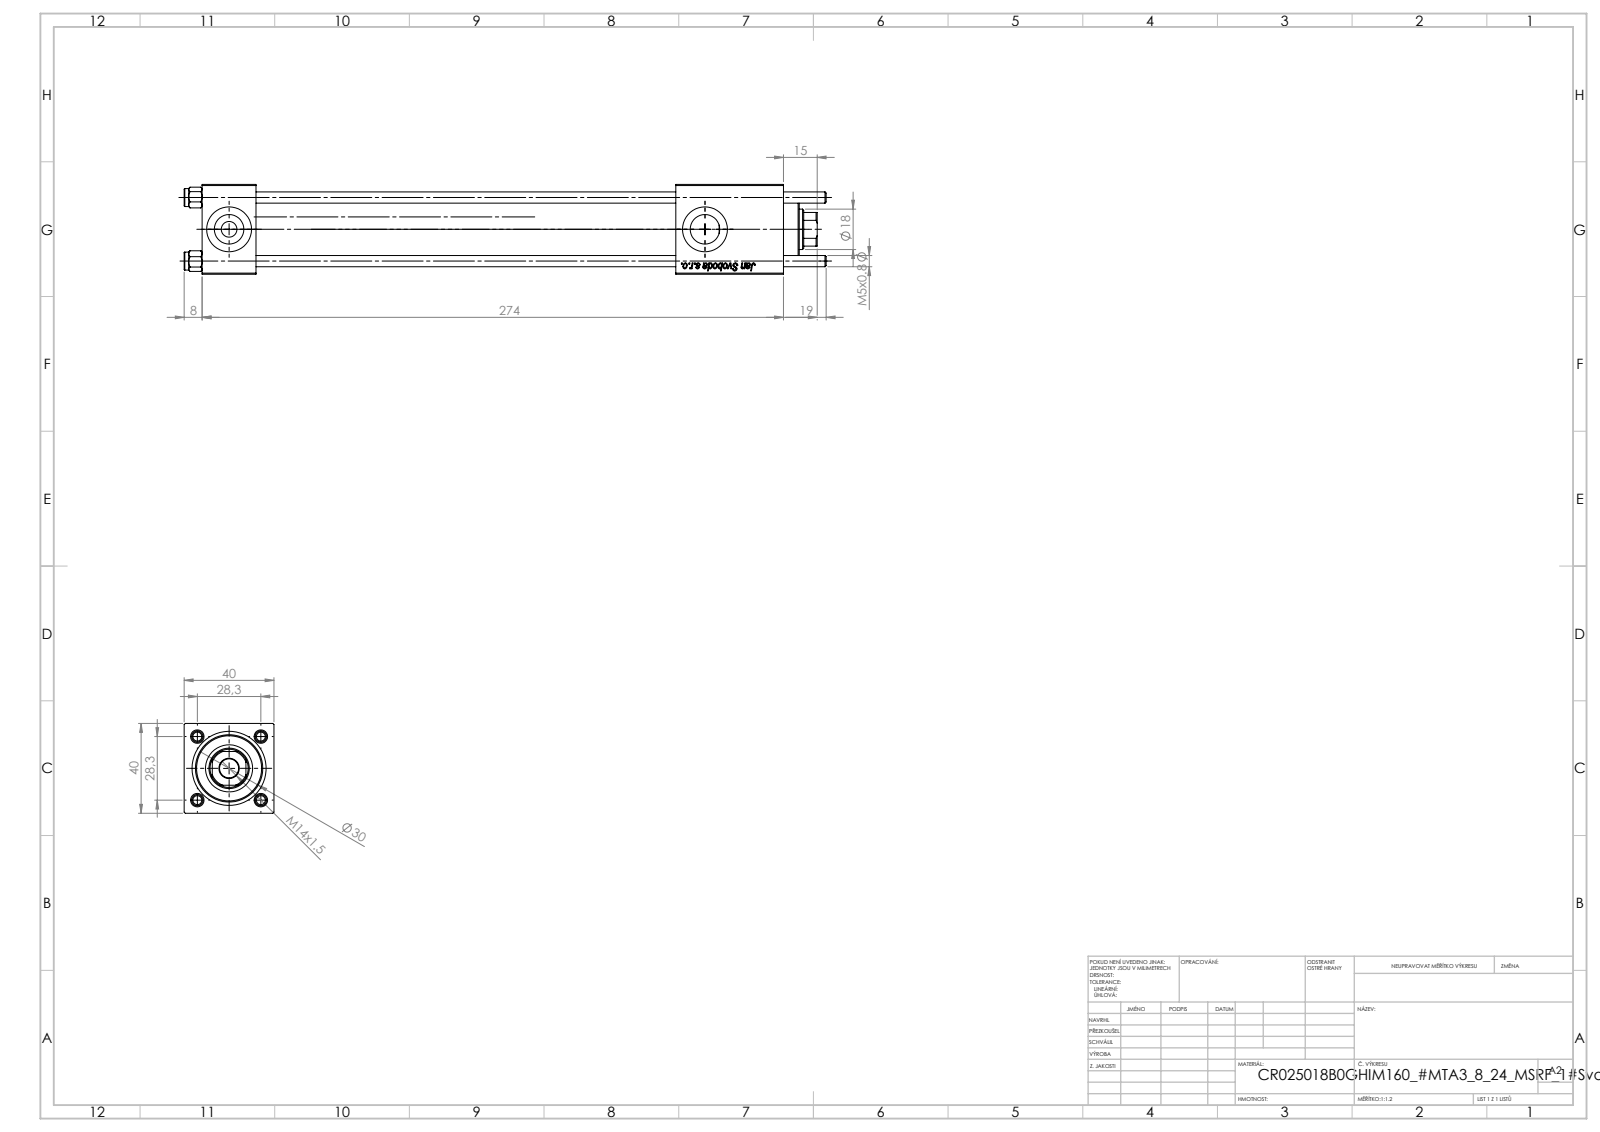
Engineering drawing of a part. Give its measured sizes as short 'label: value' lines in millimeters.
name: V215CR_VCP_B; V215CR_B_TYCINKA; V215_VC_A; V215CR_B-1 (+1 more)
written by: SolidWorks 2019 (CONFIG_CONTROL_DESIGN)
unit: mm
bodies: 11 solids, 1152 faces (428 planar, 76 cylindrical, 648 other)
size: 286 × 40 × 40
volume: 236 057 mm³; area: 102 238 mm²
holes: 4× ⌀5, 3× ⌀20, 2× ⌀7, 2× ⌀13.16, 1× ⌀8.5, 1× ⌀18, 1× ⌀21, 1× ⌀25, 1× ⌀30
bosses: 4× ⌀8, 1× ⌀31
rounds: 1× R8.5
face distances: 40, 24, 211, 187, 230.3, 206.3, 19.3, 259, 235, 48
hole spacings: 20.01, 28.3, 40.02, 212
